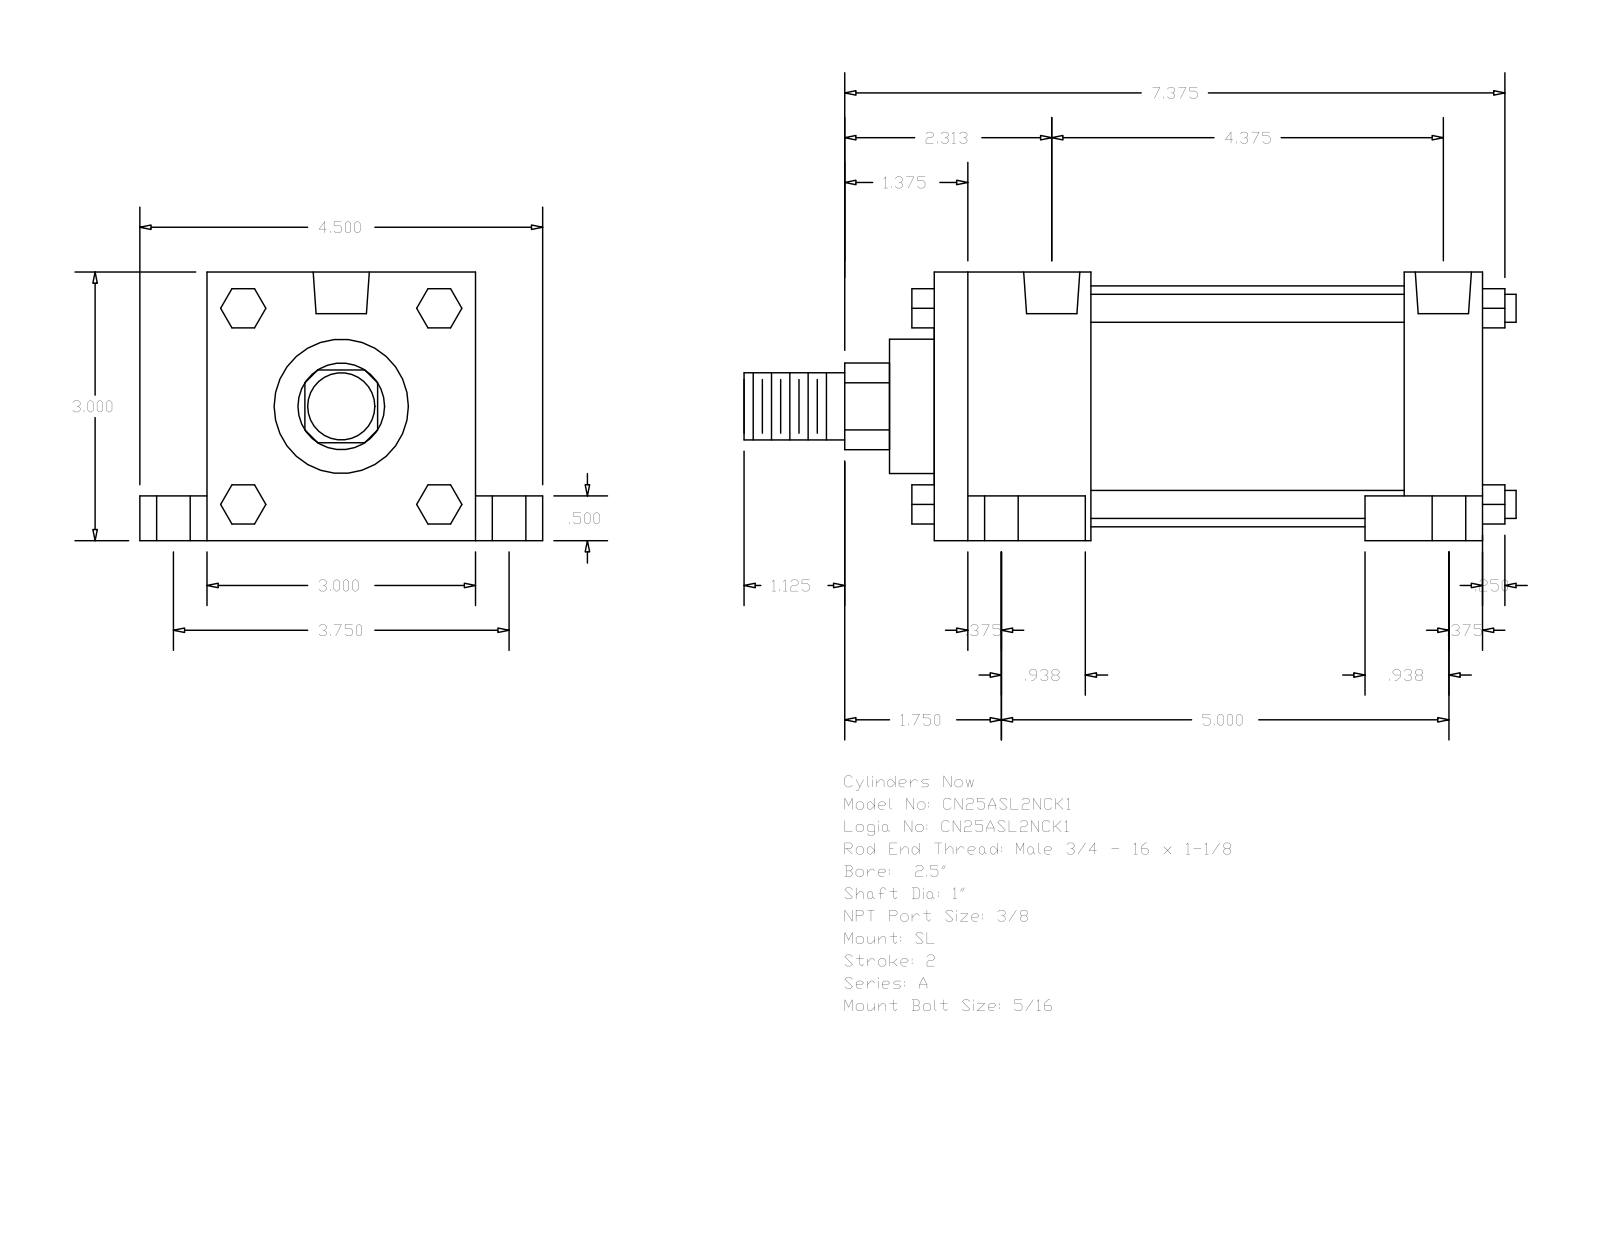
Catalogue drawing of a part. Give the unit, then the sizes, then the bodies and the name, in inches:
Units: inches
Overall size (bounding box): 8.625 × 4.5 × 3
Round holes (diameter × count): ⌀0.219 ×4, ⌀0.375 ×4, ⌀0.625 ×4, ⌀0.627 ×2
Round bosses / shafts (diameter × count): ⌀0.313 ×4, ⌀2.69 ×1, ⌀1.5 ×1, ⌀1 ×1, ⌀0.75 ×1
Partial cylindrical surfaces — rounded edges, fillets, slot ends (radius × count): R0.484 ×1
Main face-to-face distances: 3, 6.125, 0.5, 0.875, 1.75, 4.375, 5.25, 3.5, 0.75, 2.5
Hole centre spacings: 0.094, 1.875, 1.876, 1.933, 1.957, 3.75, 4.469, 4.562
Bodies: 0 solids, 148 faces (112 planar, 36 cylindrical, 0 other)
Part name (STEP PRODUCT): A_SL__0250_1
STEP written by: GSSL Pune (CONFIG_CONTROL_DESIGN)
